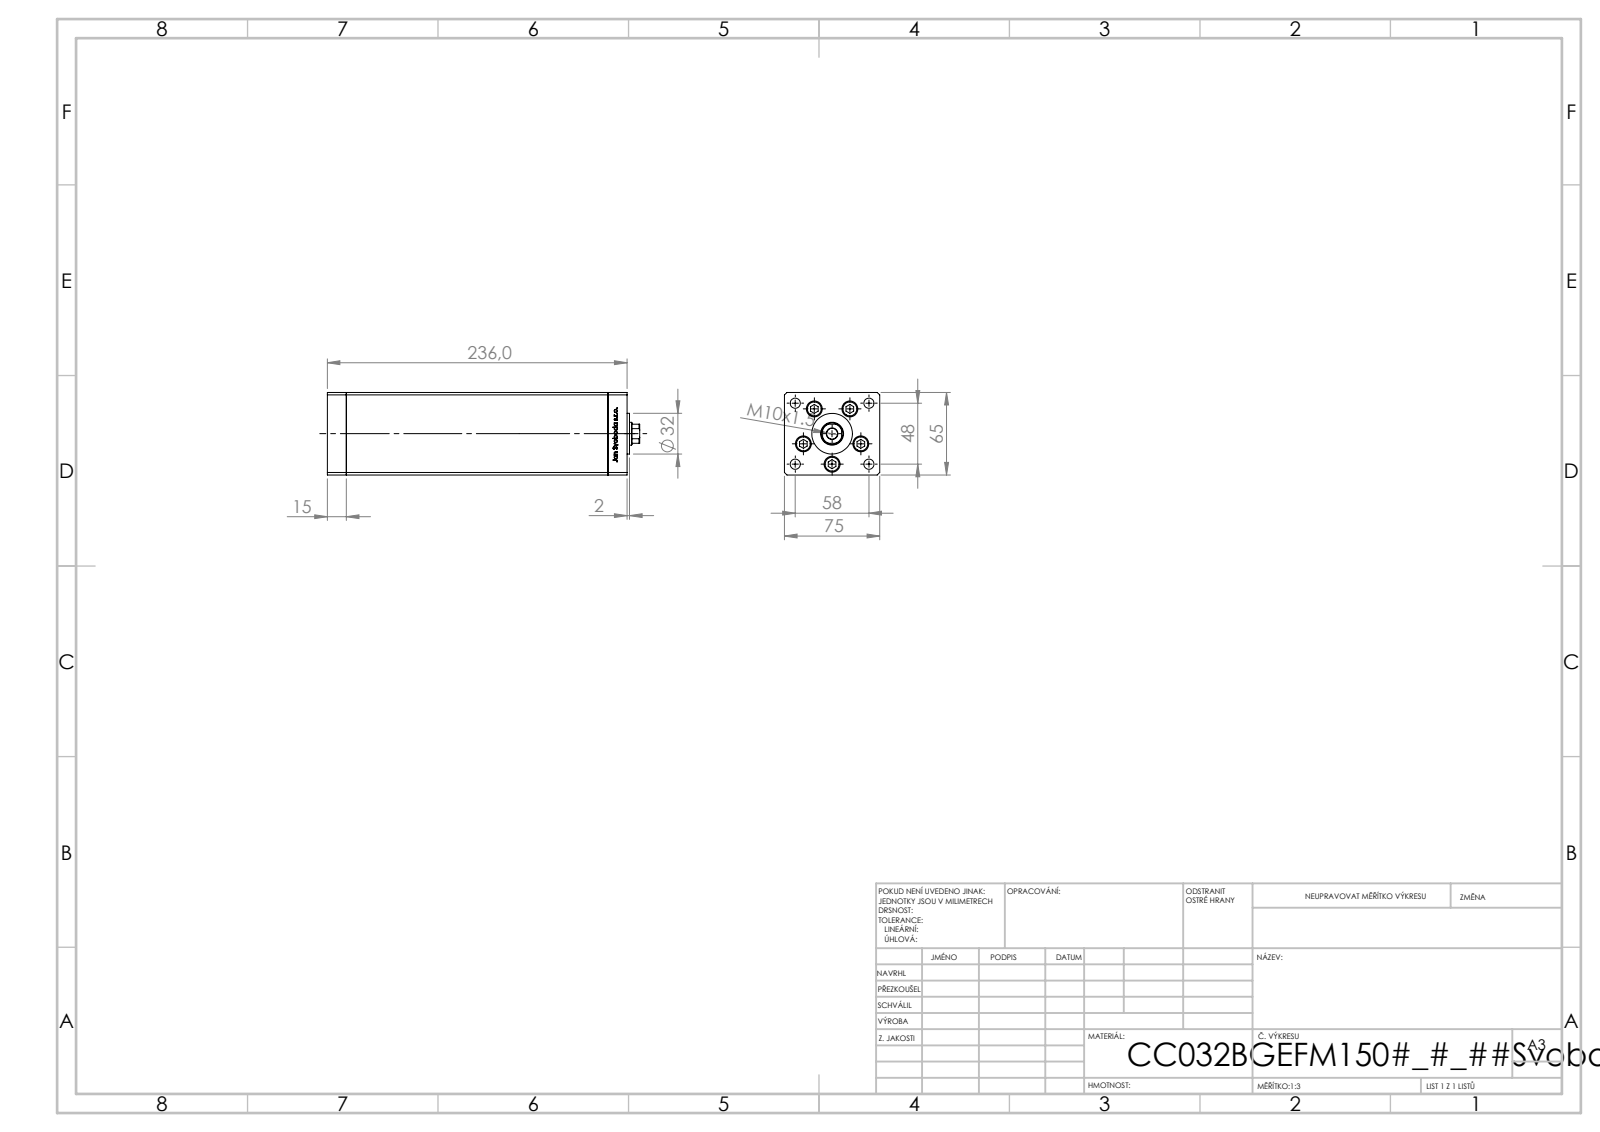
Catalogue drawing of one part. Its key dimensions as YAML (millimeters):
part_name: "V220C_FRONT_B; V220C_B MIDDLE; V220C_VC_B; V220C BACK_B (+1 more)"
step_written_by: "SolidWorks 2019 (CONFIG_CONTROL_DESIGN)"
units: millimeters
bodies: {solids: 14, faces: 1183, planar: 462, cylindrical: 147, other: 574}
overall_size: [246, 75, 65]
volume: 1011000
surface_area: 159331
round_holes:
  - {diameter: 9, count: 5}
  - {diameter: 12.5, count: 5}
  - {diameter: 8, count: 4}
  - {diameter: 2, count: 2}
  - {diameter: 13.16, count: 2}
  - {diameter: 8.5, count: 1}
  - {diameter: 18, count: 1}
round_bosses_or_shafts:
  - {diameter: 8, count: 5}
  - {diameter: 32, count: 1}
partial_cylinders:
  - {radius: 0.93, count: 2}
  - {radius: 8.5, count: 1}
face_to_face_distances: [75, 65, 15, 206, 221, 236, 54.5, 10.5, 26.25, 48.75]
hole_center_spacings: [24, 37.64, 15.67, 17.22, 27.71, 28.83, 29, 32.63]
